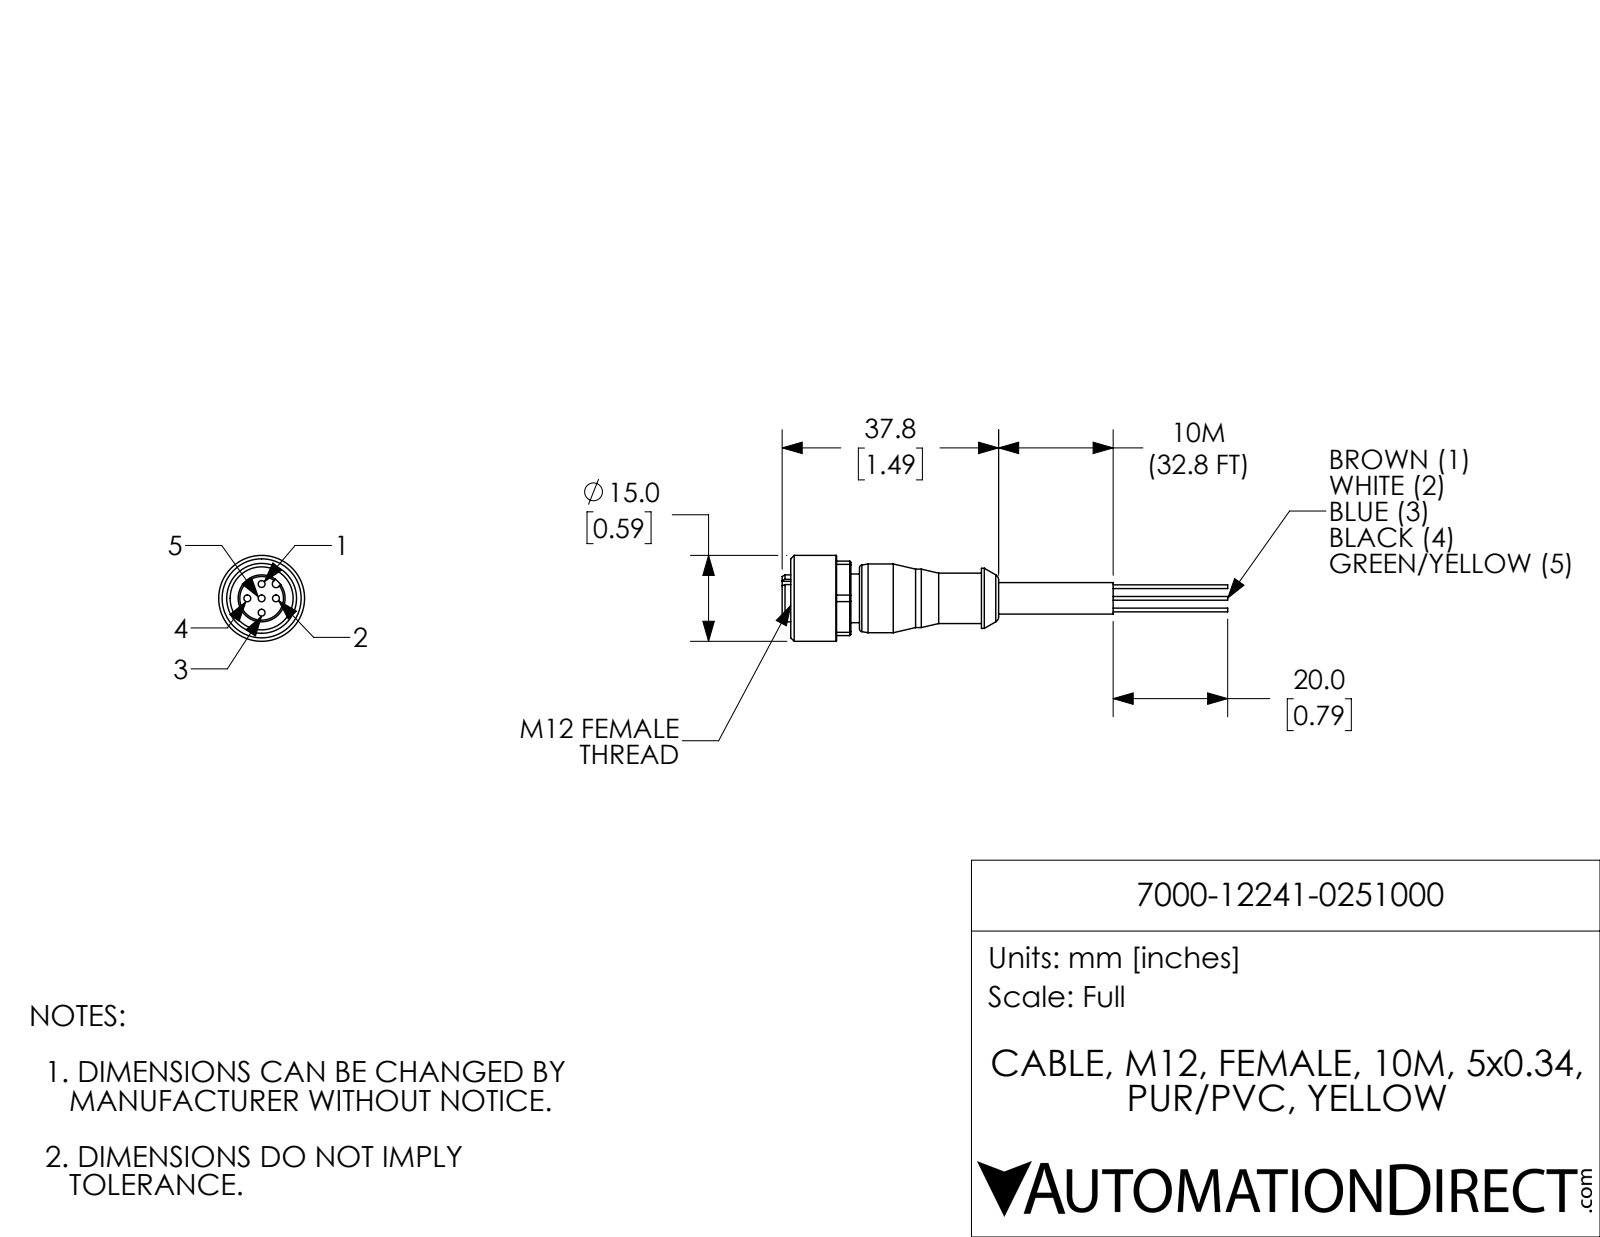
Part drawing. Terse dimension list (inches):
name: 7000-12241-0251000
written by: SolidWorks 2017 (AUTOMOTIVE_DESIGN)
unit: in
bodies: 1 solid, 106 faces (34 planar, 45 cylindrical, 27 other)
size: 3.063 × 0.591 × 0.591
volume: 0.248 in³; area: 4.45 in²
holes: 5× ⌀0.047, 1× ⌀0.433
bosses: 5× ⌀0.026, 1× ⌀0.591, 1× ⌀0.472, 1× ⌀0.413, 1× ⌀0.402, 1× ⌀0.346, 1× ⌀0.335, 1× ⌀0.323
rounds: 1× R0.026, 1× R0.283
face distances: 0.472, 0.059, 0.118, 0.512, 0.354, 1.016, 0.295, 0.413, 0.098, 0.531
hole spacings: 0.098, 0.139, 0.197
